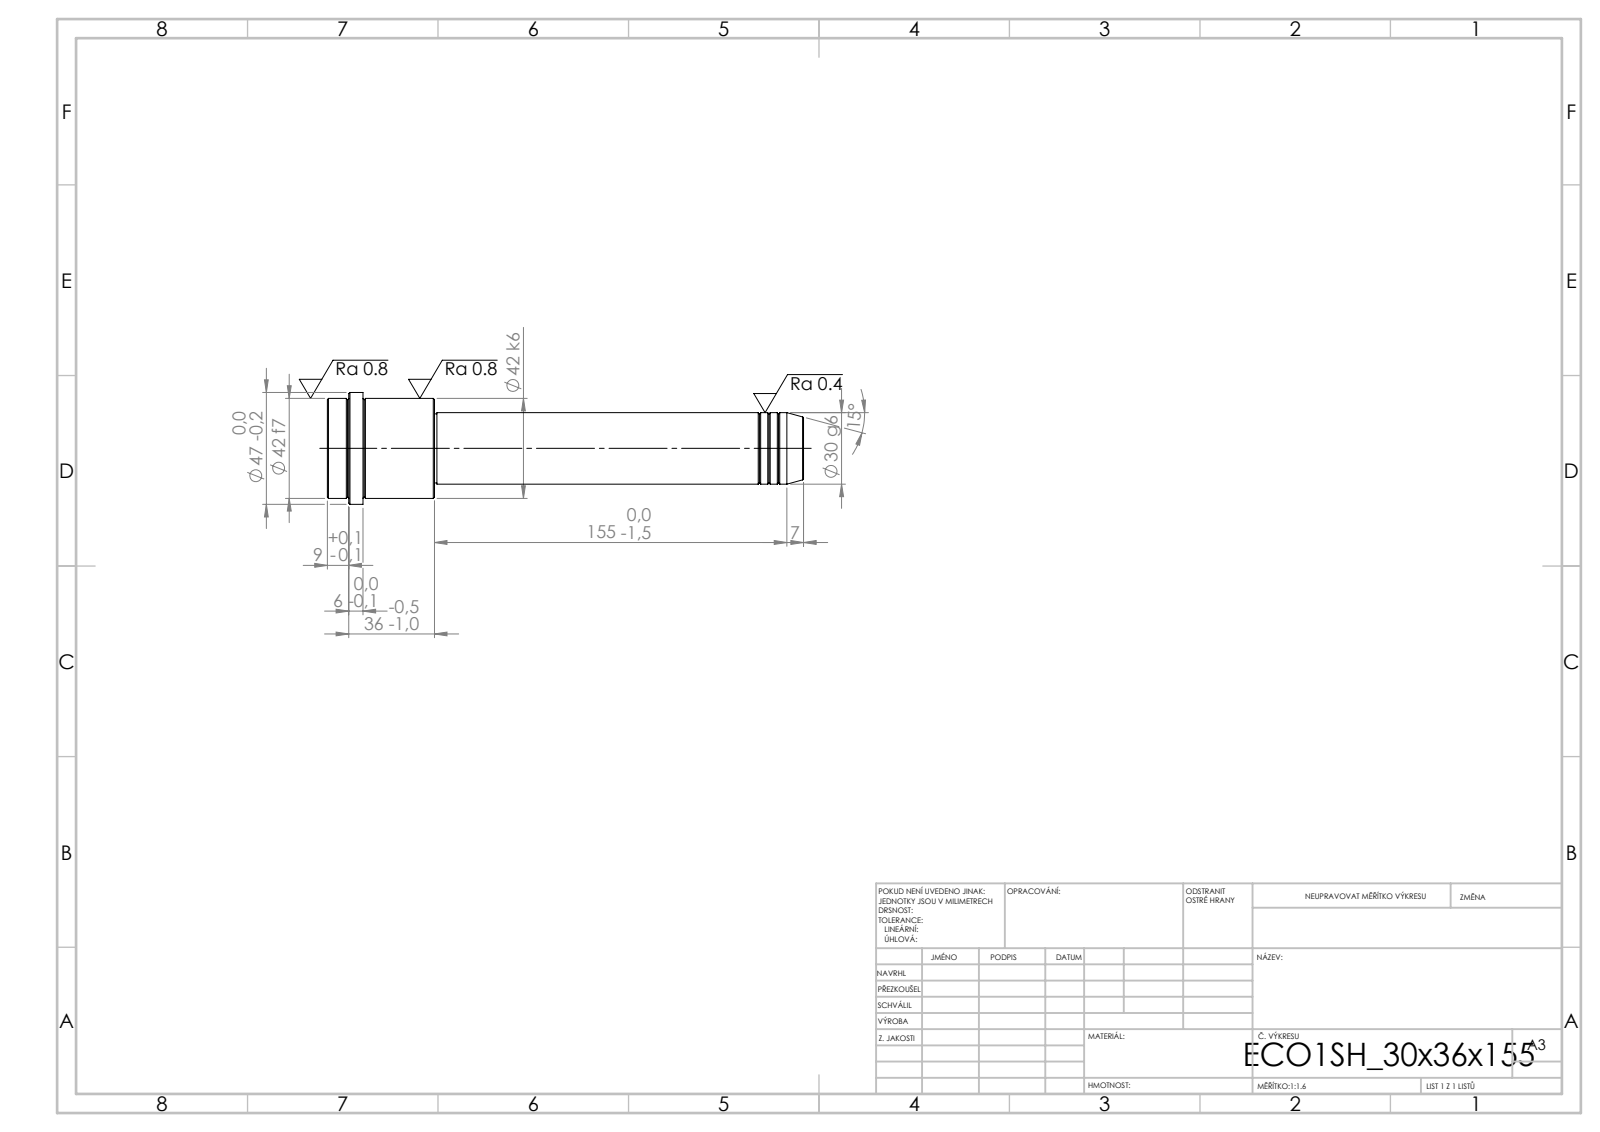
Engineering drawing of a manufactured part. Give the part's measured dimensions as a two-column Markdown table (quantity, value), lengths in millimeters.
| quantity | value |
| --- | --- |
| STEP written by | SolidWorks 2019 (CONFIG_CONTROL_DESIGN) |
| units | millimeters |
| bodies | 1 solid, 52 faces (6 planar, 16 cylindrical, 30 other) |
| overall size | 200 × 47 × 47 |
| volume | 173 100 mm³ |
| surface area | 24 180 mm² |
| round bosses / shafts (diameter × count) | 47 × 1, 42 × 1, 30 × 1, 29 × 1 |
| main face-to-face distances | 45, 155, 200, 185, 30, 15, 191, 36, 6, 9 |
